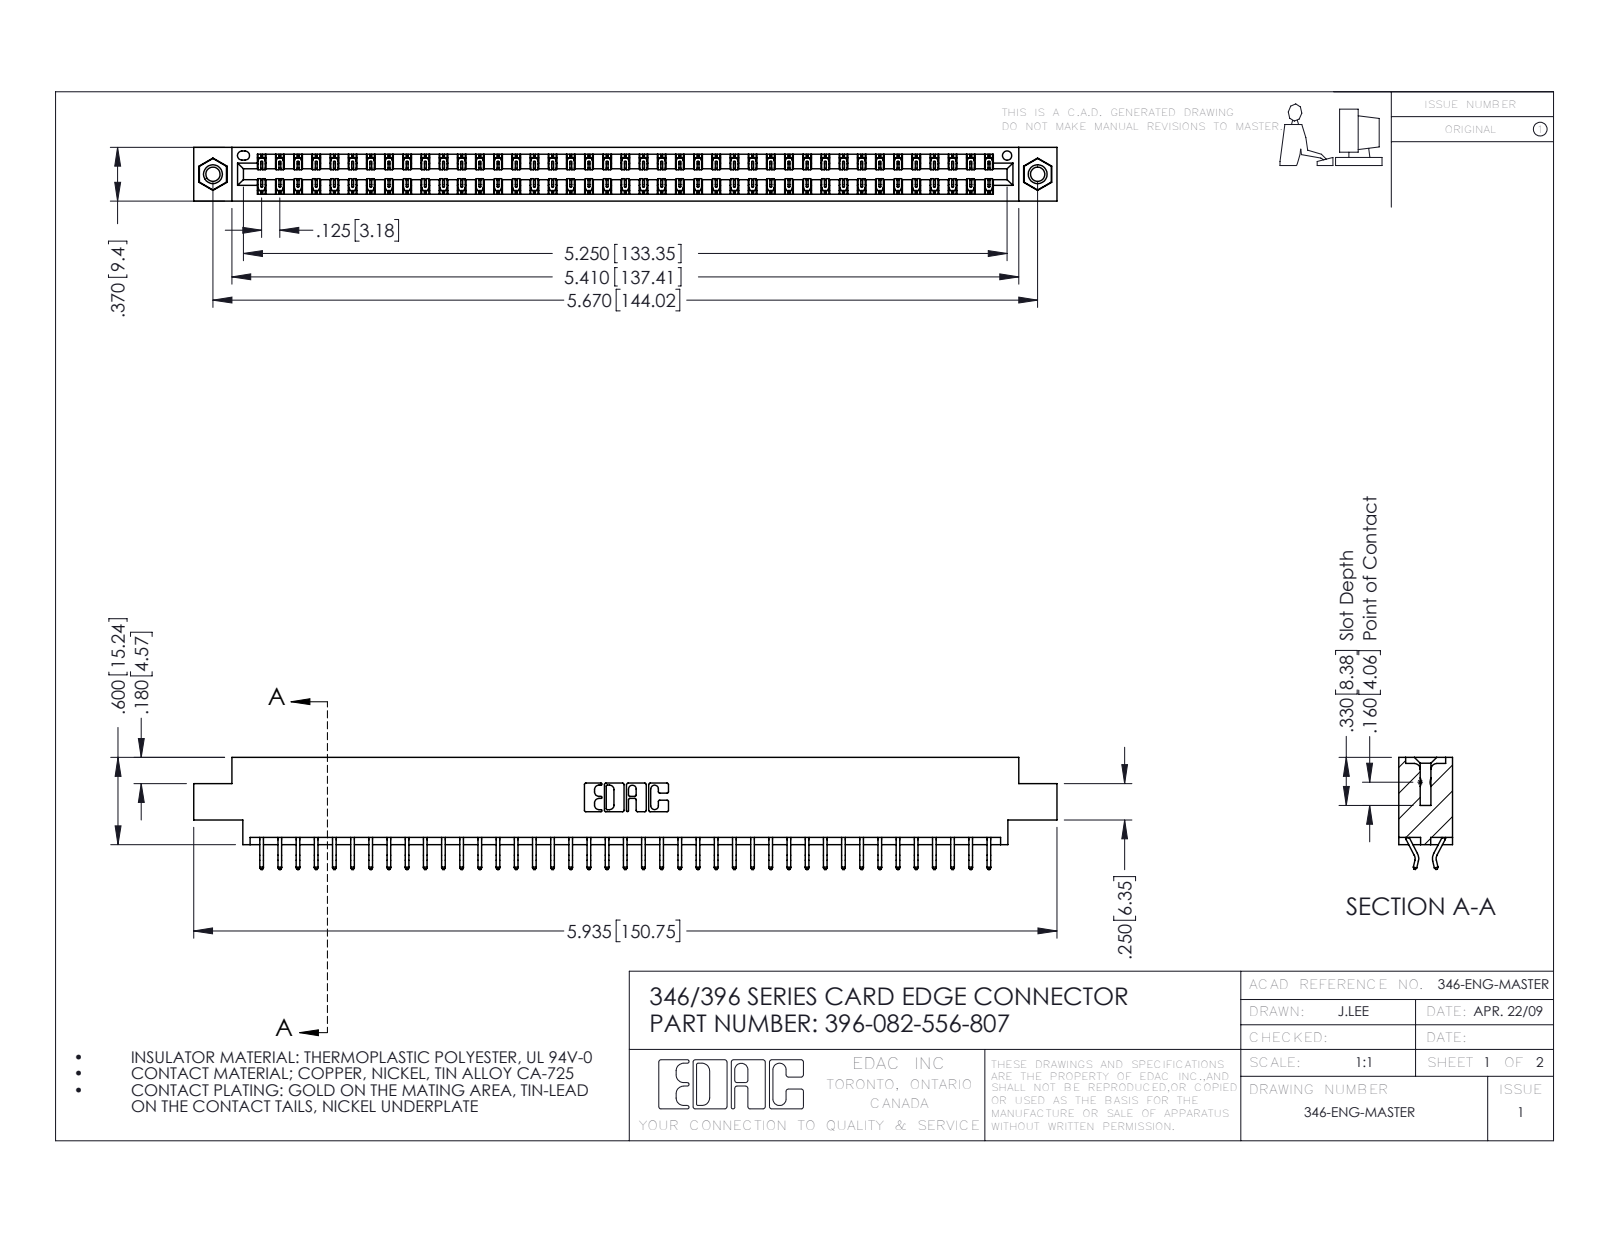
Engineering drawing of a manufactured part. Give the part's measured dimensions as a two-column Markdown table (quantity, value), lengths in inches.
| quantity | value |
| --- | --- |
| part name | 345-250-001_345-250-005-103; 346 Part_0.170 Offset - 0.156 Dia-TI; 345-292-001_556 Tail; 396-082-556-807 |
| STEP written by | SolidWorks 2016 (CONFIG_CONTROL_DESIGN) |
| units | inches |
| bodies | 85 solids, 4942 faces (3310 planar, 1616 cylindrical, 16 other) |
| overall size | 5.935 × 0.77 × 0.37 |
| volume | 0.886 in³ |
| surface area | 31.13 in² |
| round holes (diameter × count) | 0.098 × 2, 0.125 × 2, 0.156 × 2, 0.064 × 1 |
| round bosses / shafts (diameter × count) | 0.155 × 2 |
| partial cylindrical surfaces (radius × count) | 0.006 × 123, 0.01 × 22, 0.007 × 6, 0.031 × 6, 0.026 × 3, 0.01 × 2, 0.014 × 2, 0.022 × 2 |
| main face-to-face distances | 0.048, 0.322, 0.37, 0.25, 0.025, 0.072, 0.298, 0.275, 0.222, 0.148 |
| hole center spacings | 0.246, 5.461, 5.67 |
